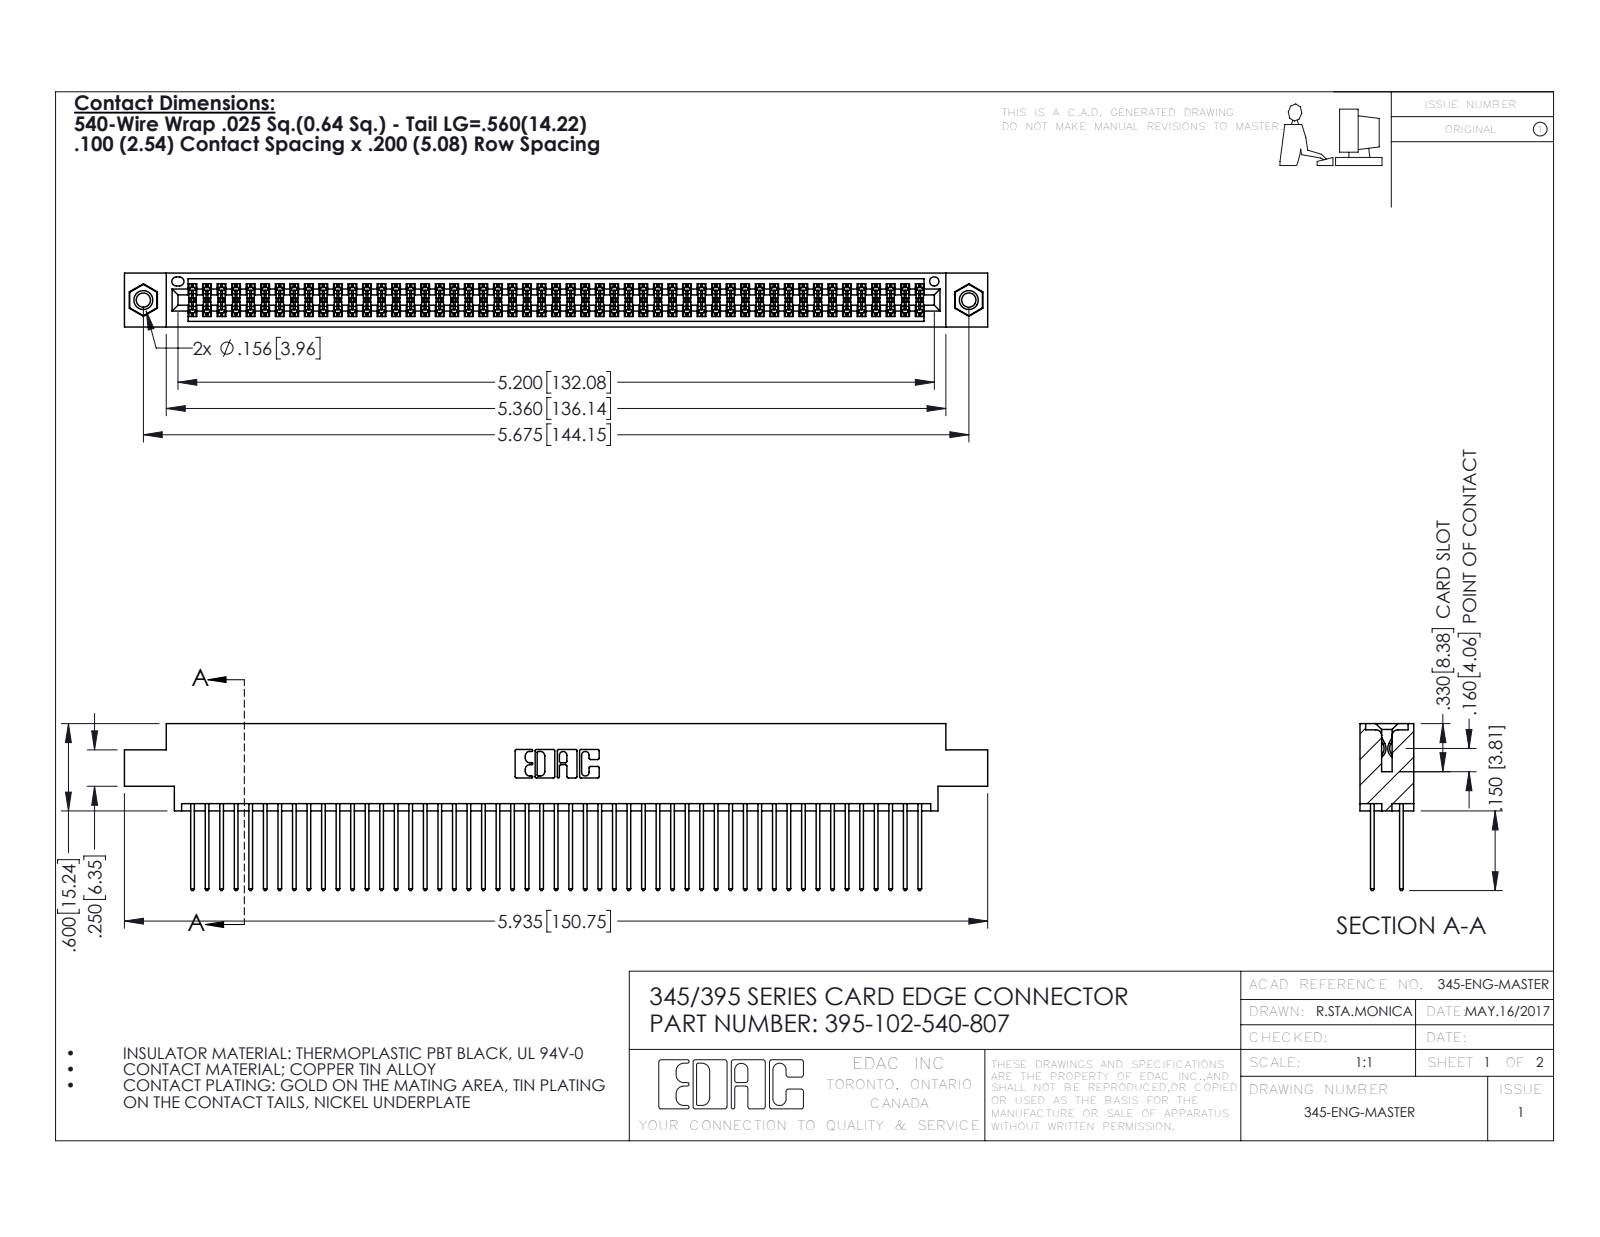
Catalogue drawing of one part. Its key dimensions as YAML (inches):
part_name: "345-250-001_345-250-005-103; 345 Part_0.170 Offset - 0.156 Dia-TI; 395-102-540-807; 345-292-001_345-293-140"
step_written_by: "SolidWorks 2016 (CONFIG_CONTROL_DESIGN)"
units: inches
bodies: {solids: 105, faces: 5290, planar: 3482, cylindrical: 1792, other: 16}
overall_size: [5.935, 1.147, 0.37]
volume: 0.915
surface_area: 37.65
round_holes:
  - {diameter: 0.098, count: 2}
  - {diameter: 0.125, count: 2}
  - {diameter: 0.156, count: 2}
  - {diameter: 0.064, count: 1}
round_bosses_or_shafts:
  - {diameter: 0.155, count: 2}
partial_cylinders:
  - {radius: 0.006, count: 153}
  - {radius: 0.01, count: 102}
  - {radius: 0.01, count: 22}
  - {radius: 0.007, count: 6}
  - {radius: 0.031, count: 6}
  - {radius: 0.026, count: 3}
  - {radius: 0.014, count: 2}
  - {radius: 0.019, count: 2}
face_to_face_distances: [0.072, 0.298, 0.2, 0.098, 0.272, 0.025, 0.37, 0.225, 0.175, 0.149]
hole_center_spacings: [0.27, 5.439, 5.675]
